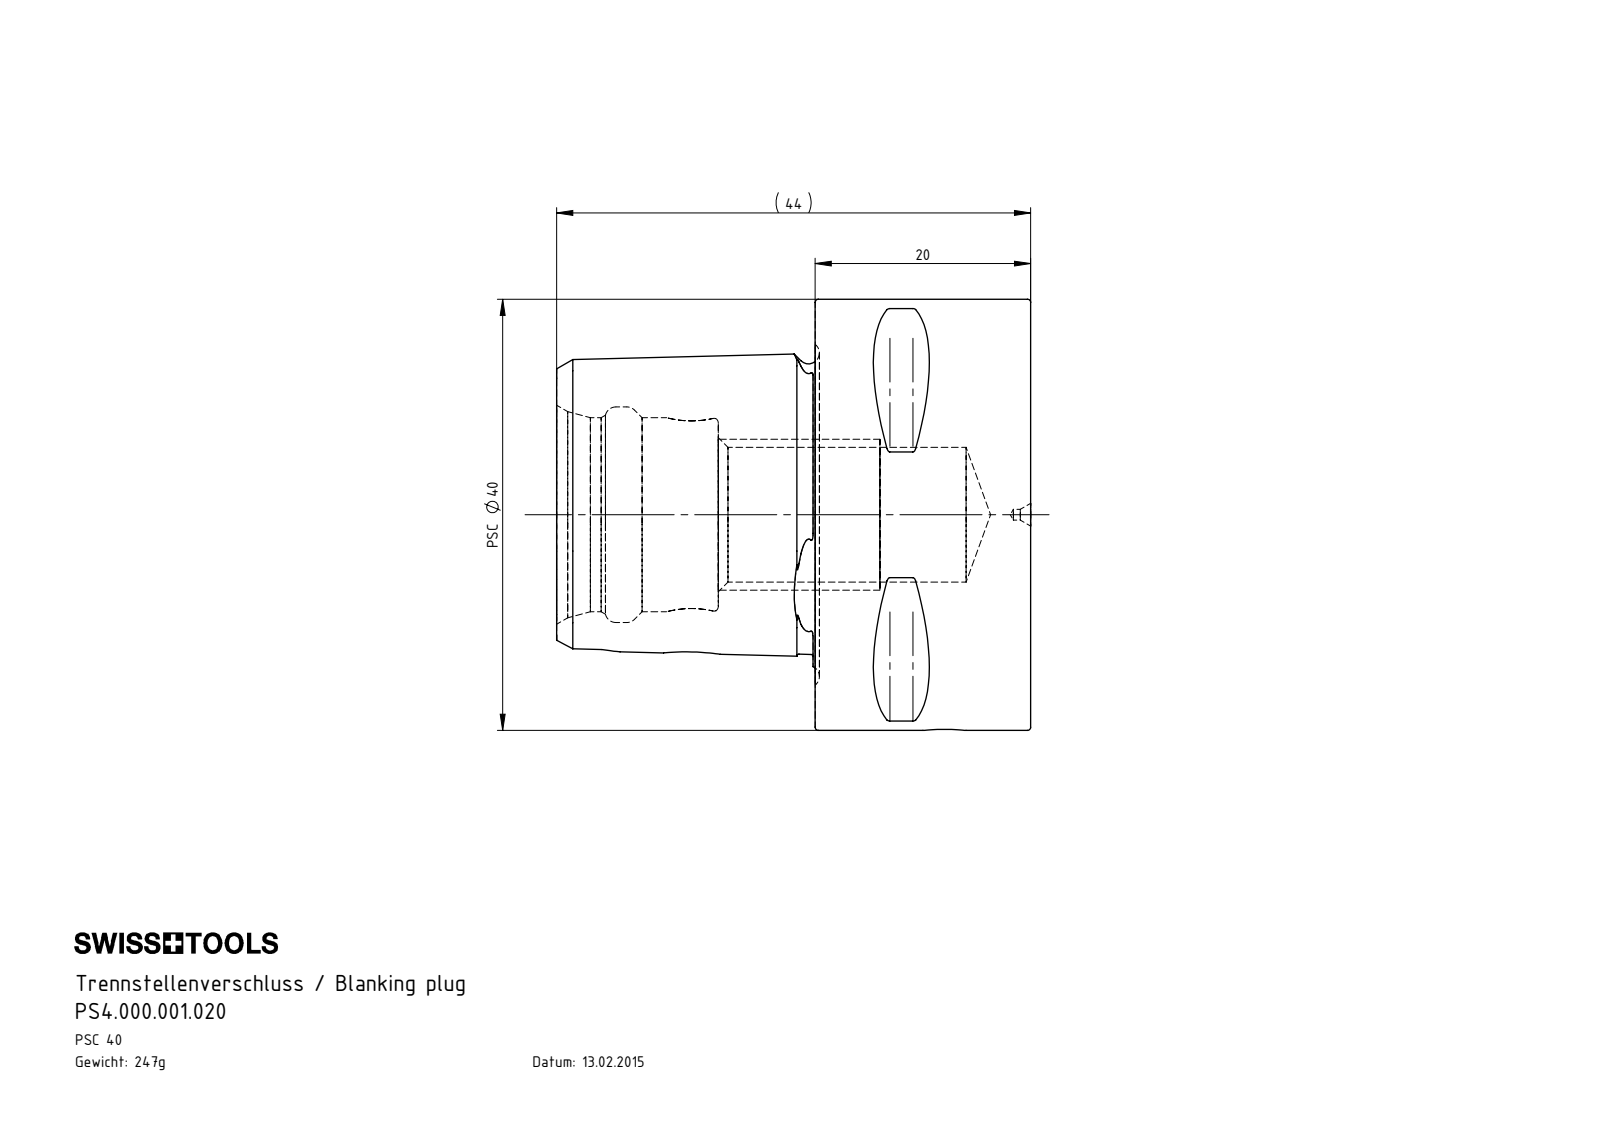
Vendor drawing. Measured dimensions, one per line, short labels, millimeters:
name: PS4.000.001.020
written by: SolidWorks 2017 (AUTOMOTIVE_DESIGN)
unit: mm
bodies: 1 solid, 93 faces (19 planar, 18 cylindrical, 56 other)
size: 44 × 40 × 40
volume: 31 450 mm³; area: 8 957 mm²
holes: 1× ⌀1, 1× ⌀4, 1× ⌀4.6, 1× ⌀12.5, 1× ⌀18, 1× ⌀20
bosses: 1× ⌀40
rounds: 8× R0.3, 1× R3
face distances: 20, 24, 44, 15.52, 35.3, 15, 9, 29, 23.8, 8.8
hole spacings: 23.5
